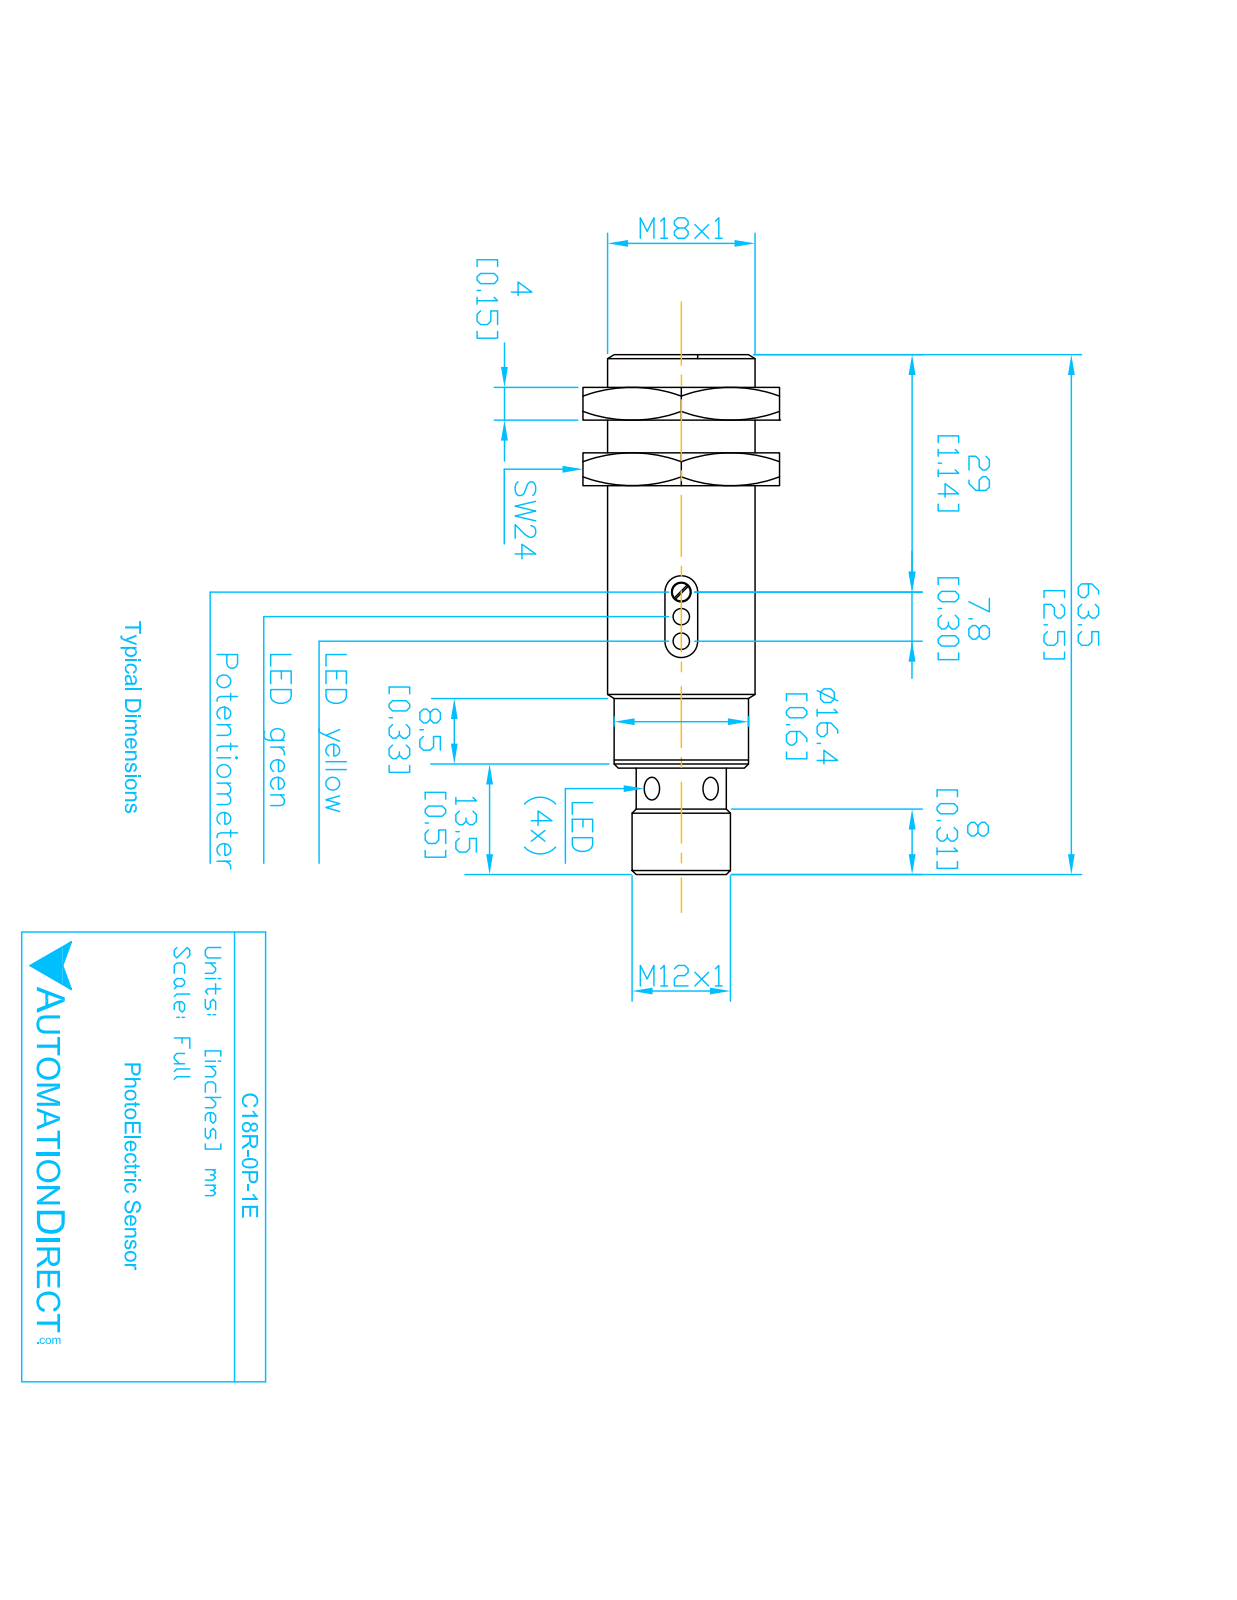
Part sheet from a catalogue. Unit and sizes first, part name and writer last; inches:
Units: inches
Overall size (bounding box): 2.5 × 0.709 × 0.709
Round holes (diameter × count): ⌀0.118 ×3, ⌀0.335 ×1
Round bosses / shafts (diameter × count): ⌀0.04 ×4, ⌀0.709 ×1, ⌀0.646 ×1, ⌀0.459 ×1, ⌀0.415 ×1
Partial cylindrical surfaces — rounded edges, fillets, slot ends (radius × count): R0.02 ×2, R0.089 ×2, R0.185 ×1, R0.2 ×1
Main face-to-face distances: 2.157, 2.047, 0.11, 0.039, 2.008, 0.15, 2.5, 0.492, 0.453, 0.343
Hole centre spacings: 1.004
Volume: 0.807 in³ · Surface area: 7.011 in²
Bodies: 6 solids, 74 faces (20 planar, 36 cylindrical, 18 other)
Part name (STEP PRODUCT): C18R-0P-1E
STEP written by: SolidWorks 2017 (AUTOMOTIVE_DESIGN)
